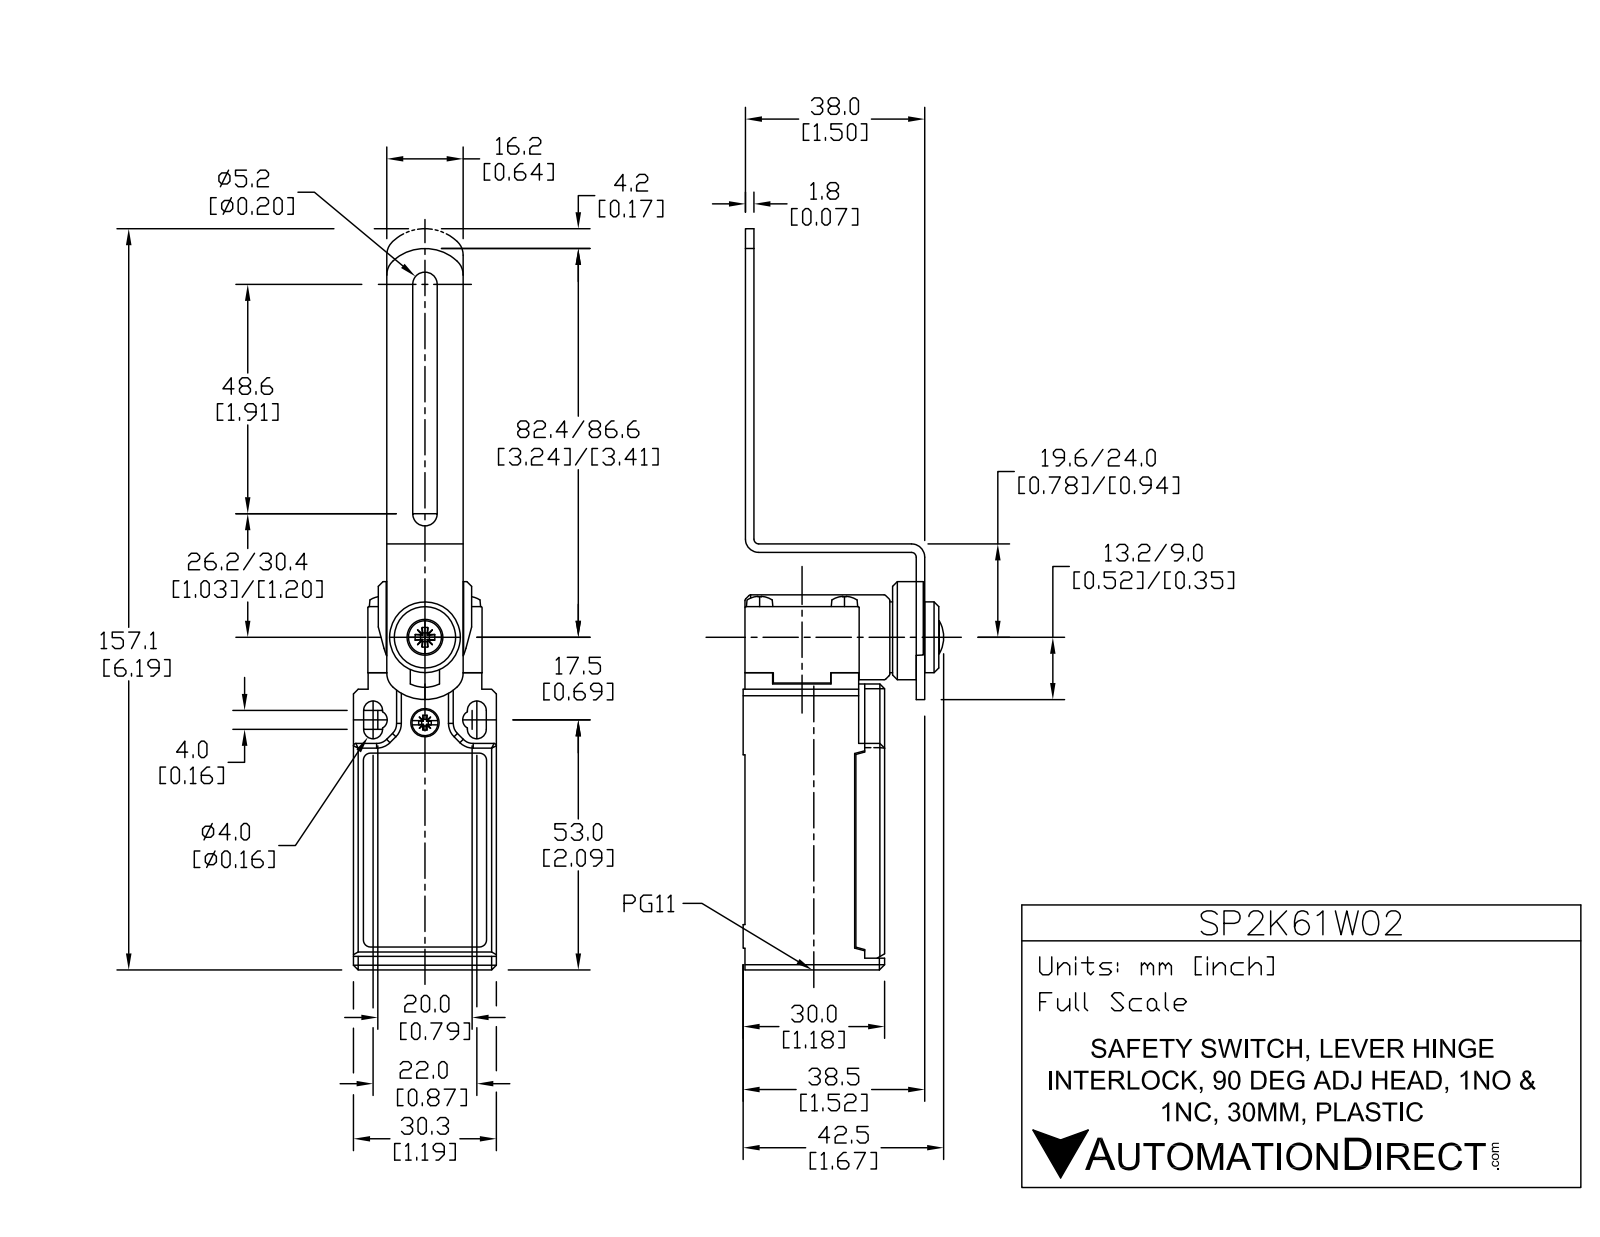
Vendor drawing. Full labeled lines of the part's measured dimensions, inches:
Part name (STEP PRODUCT): SP2K61W02
STEP written by: SolidWorks 2017 (AUTOMOTIVE_DESIGN)
Units: inches
Bodies: 5 solids, 263 faces (159 planar, 78 cylindrical, 26 other)
Overall size (bounding box): 6.122 × 1.661 × 1.193
Volume: 4.121 in³ · Surface area: 30.7 in²
Round holes (diameter × count): ⌀0.236 ×1, ⌀0.299 ×1, ⌀0.433 ×1, ⌀0.669 ×1, ⌀0.748 ×1
Round bosses / shafts (diameter × count): ⌀0.22 ×5, ⌀0.709 ×1, ⌀0.591 ×1, ⌀0.276 ×1
Partial cylindrical surfaces — rounded edges, fillets, slot ends (radius × count): R0.079 ×6, R0.02 ×4, R0.118 ×4, R0.157 ×4, R0.394 ×3, R0.039 ×2, R0.102 ×2, R0.11 ×2
Main face-to-face distances: 0.071, 1.193, 1.165, 1.425, 1.181, 0.124, 1.069, 0.945, 1.102, 0.063
Hole centre spacings: 0.713
